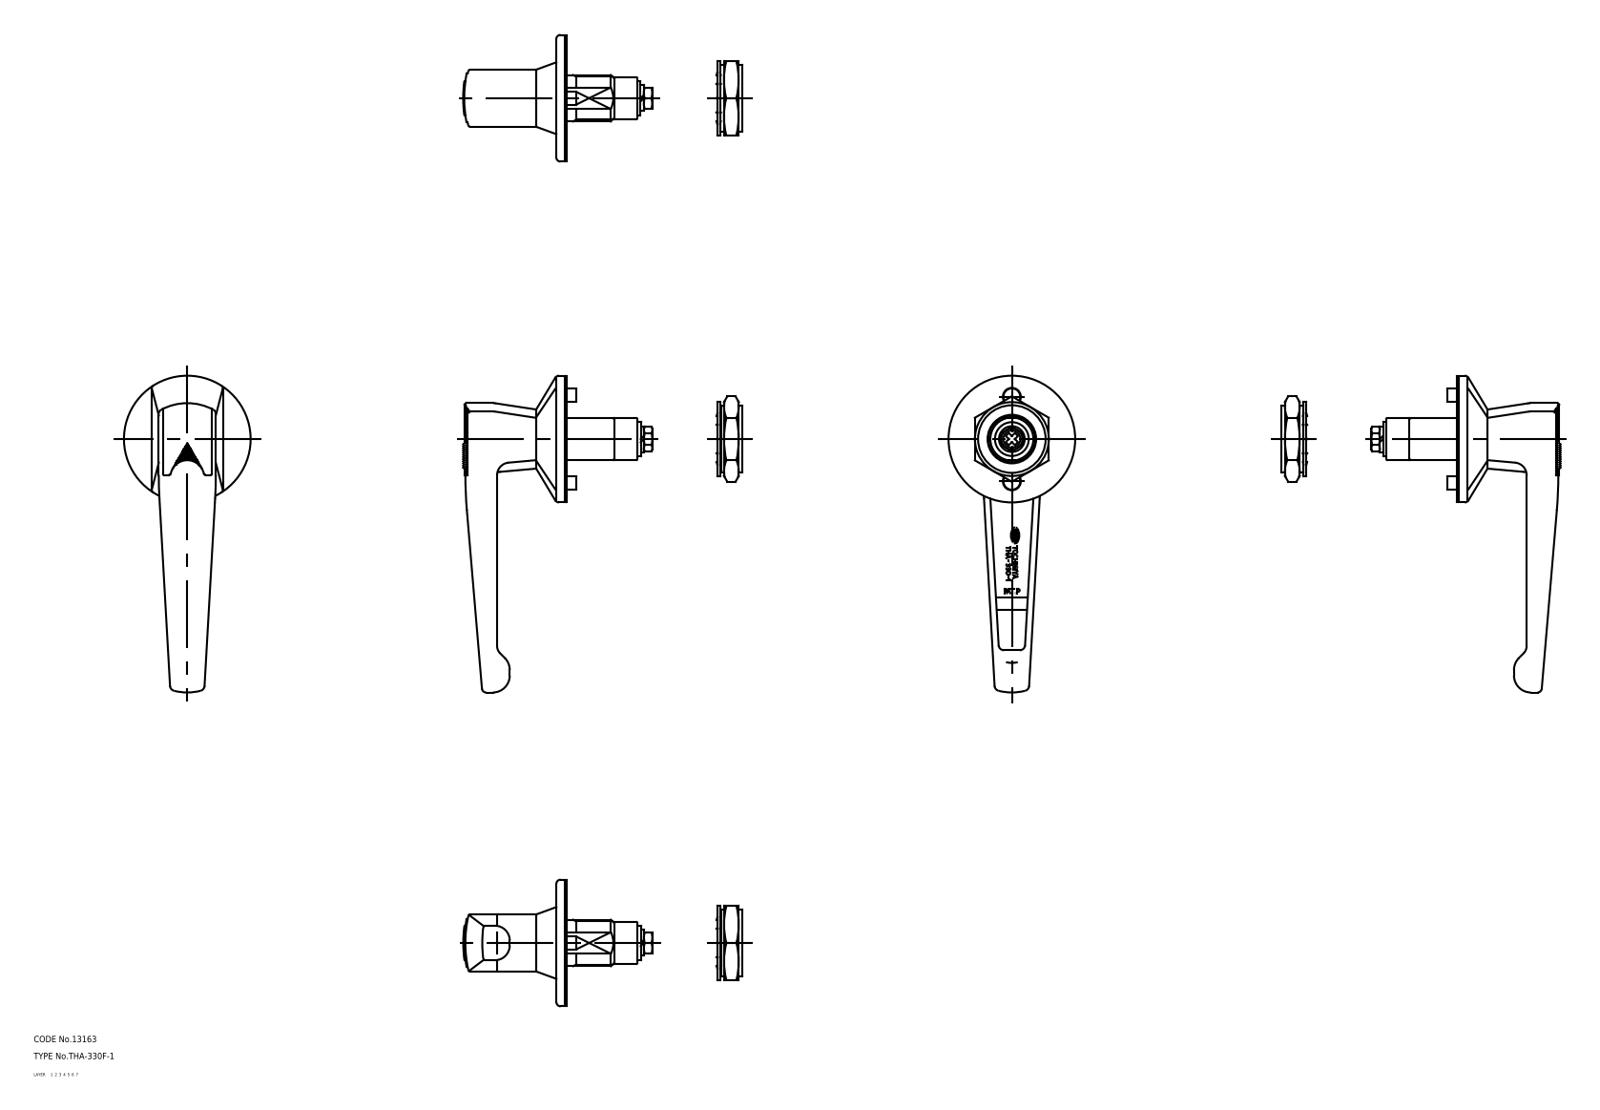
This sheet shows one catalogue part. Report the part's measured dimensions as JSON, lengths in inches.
{"part_name": "washer_B; washer_A; spacer; packing (+5 more)", "step_written_by": "CADfix (AUTOMOTIVE_DESIGN)", "units": "inches", "bodies": {"solids": 8, "faces": 296, "planar": 0, "cylindrical": 0, "other": 296}, "overall_size": [5.906, 3.526, 2.362], "volume_in3": 5.132, "surface_area_in2": 58.79}
